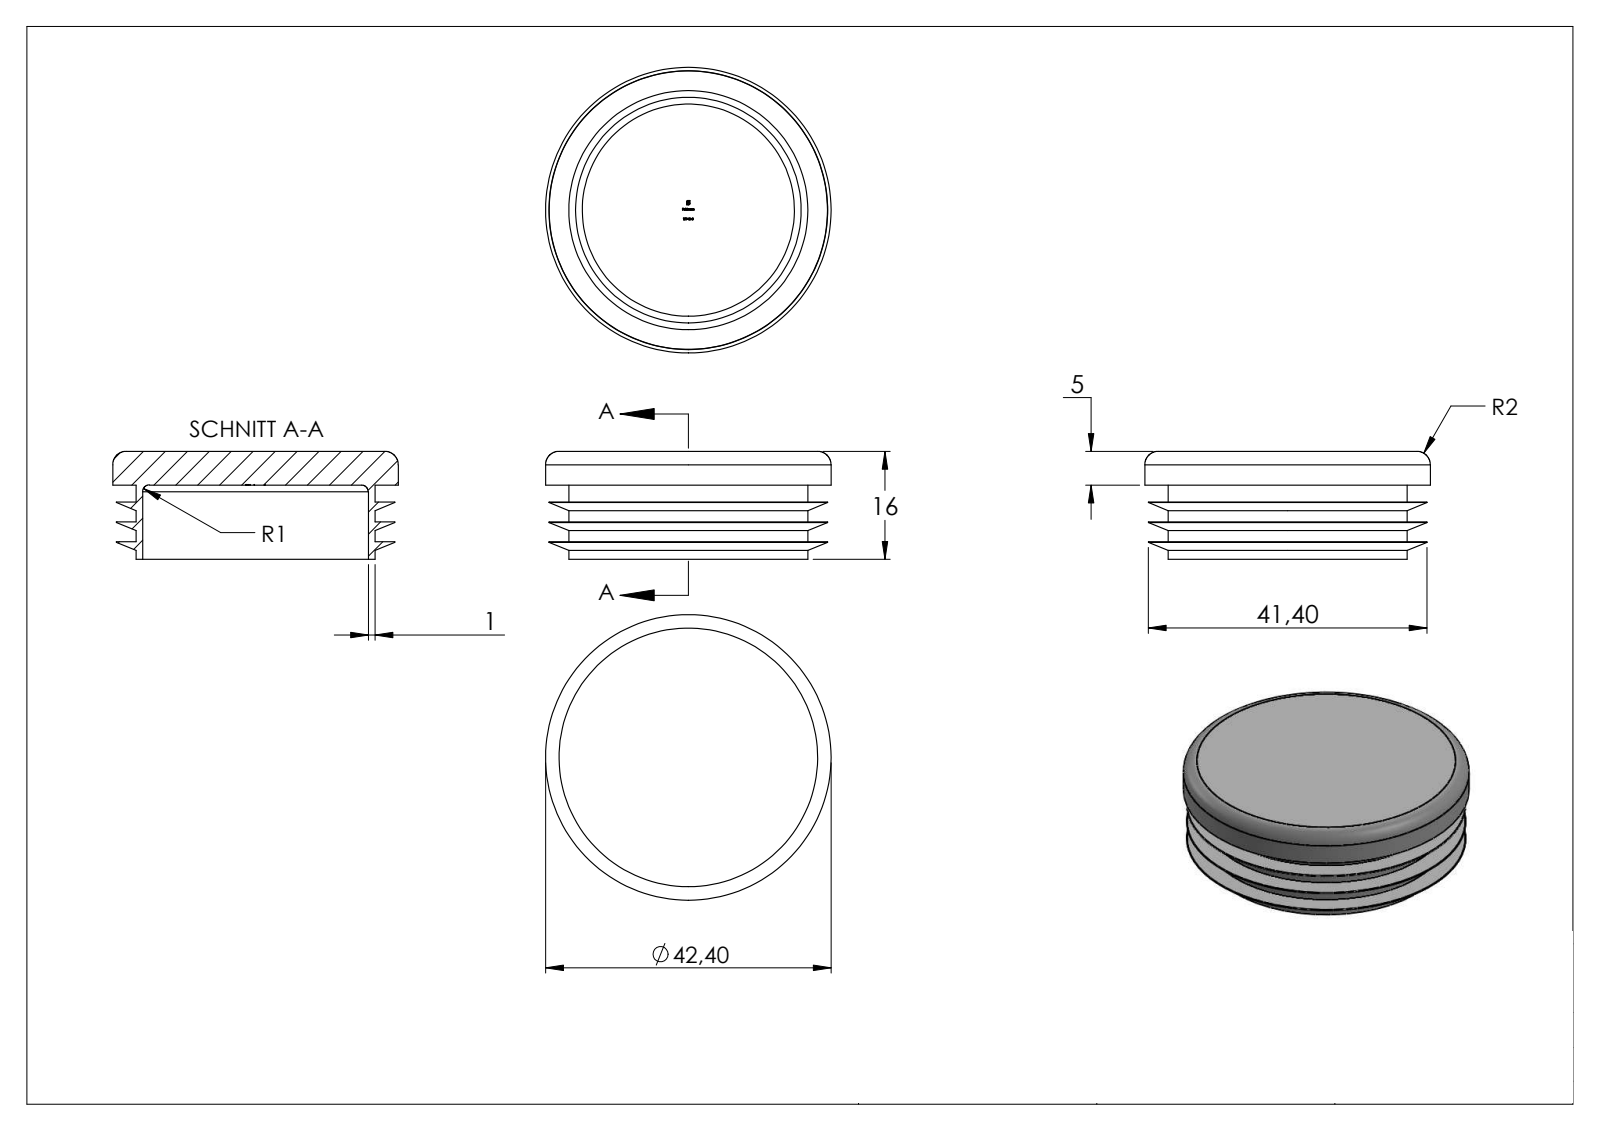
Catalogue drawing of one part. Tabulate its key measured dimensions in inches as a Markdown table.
| quantity | value |
| --- | --- |
| part name | 177-43-G |
| STEP written by | SolidWorks 2018 (CONFIG_CONTROL_DESIGN) |
| units | inches |
| bodies | 1 solid, 267 faces (148 planar, 12 cylindrical, 107 other) |
| overall size | 1.669 × 1.669 × 0.63 |
| volume | 0.542 in³ |
| surface area | 11.67 in² |
| round holes (diameter × count) | 1.319 × 1 |
| round bosses / shafts (diameter × count) | 1.669 × 1, 1.398 × 1 |
| main face-to-face distances | 0.197, 0.116, 0.215, 0.411, 0.331, 0.528, 0.232, 0.098, 0.295, 0.102 |
